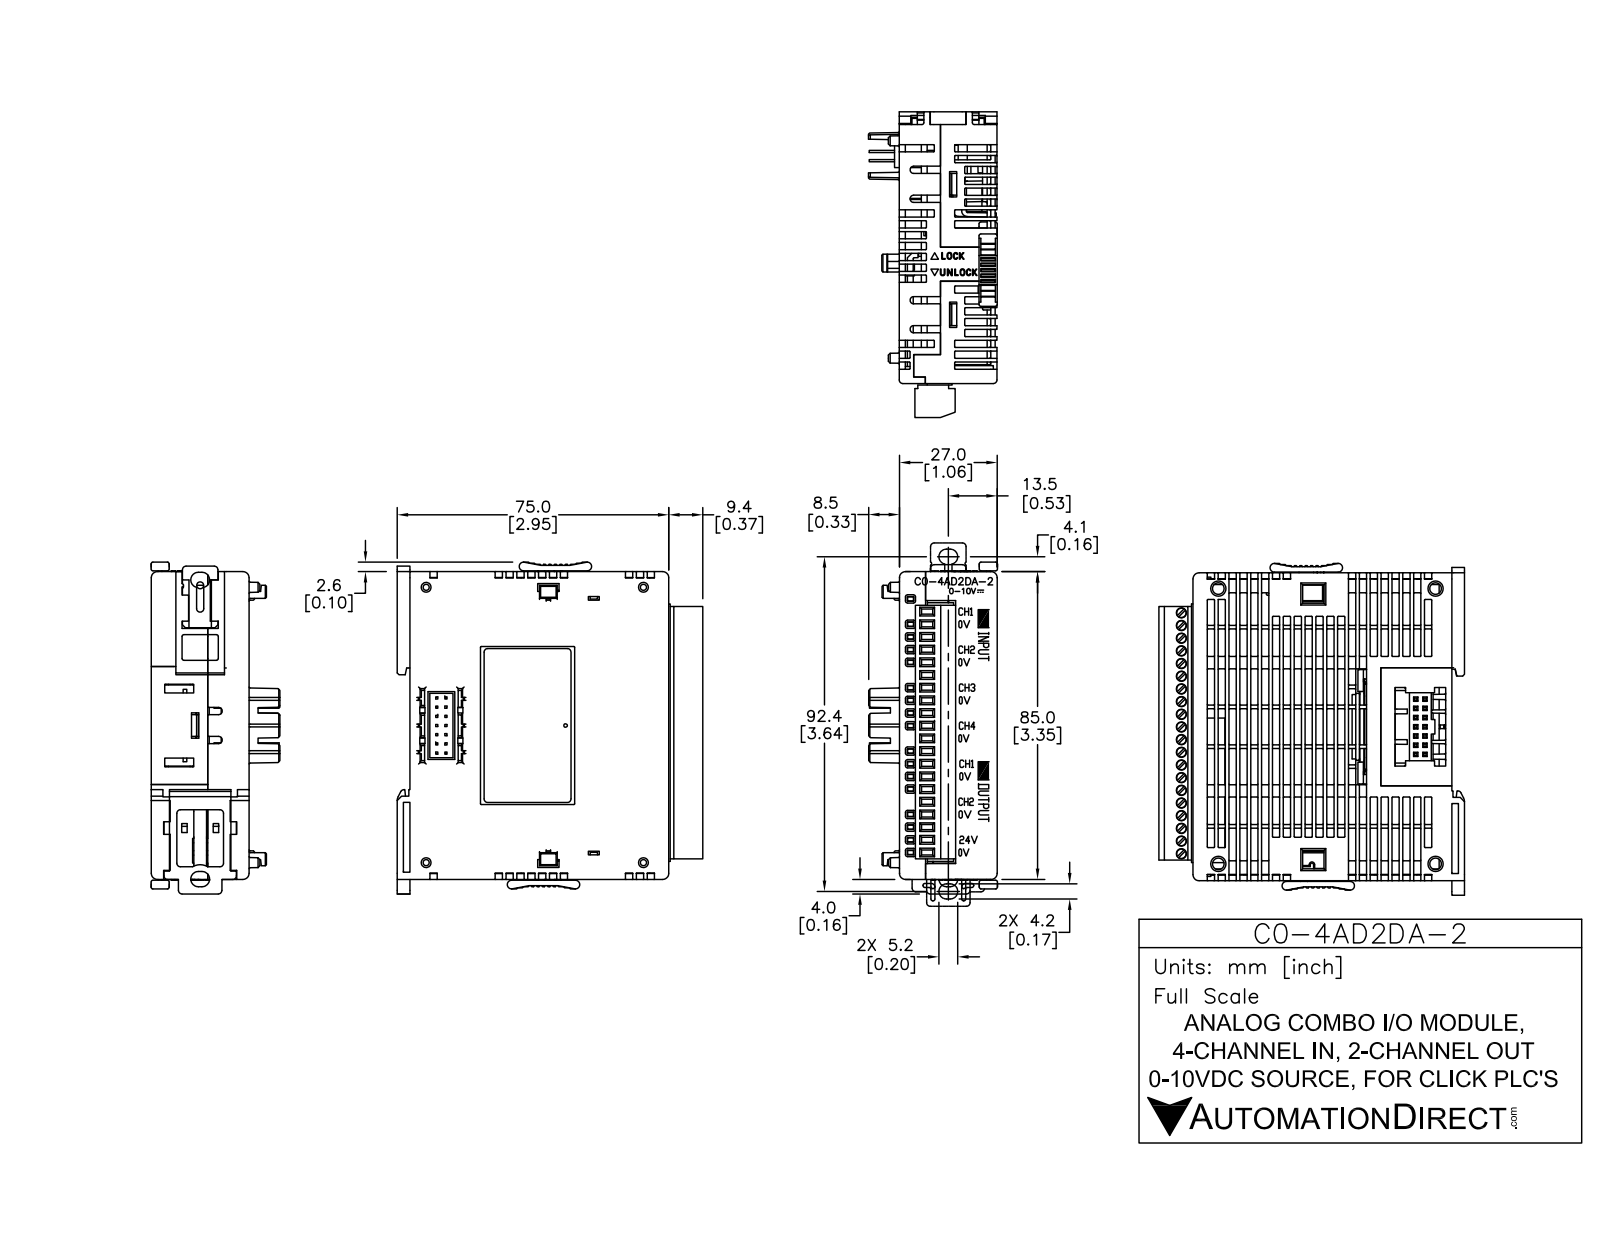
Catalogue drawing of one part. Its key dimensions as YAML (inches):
part_name: "C0-4AD2DA-2"
step_written_by: "SolidWorks 2013 (AUTOMOTIVE_DESIGN)"
units: inches
bodies: {solids: 1, faces: 4130, planar: 2924, cylindrical: 1037, other: 169}
overall_size: [3.606, 3.323, 1.4]
volume: 10.07
surface_area: 52.14
round_holes:
  - {diameter: 0.039, count: 20}
  - {diameter: 0.11, count: 20}
  - {diameter: 0.126, count: 4}
  - {diameter: 0.079, count: 2}
round_bosses_or_shafts:
  - {diameter: 0.102, count: 20}
  - {diameter: 0.075, count: 1}
partial_cylinders:
  - {radius: 0.008, count: 570}
  - {radius: 0.02, count: 43}
  - {radius: 0.012, count: 22}
  - {radius: 0.11, count: 20}
  - {radius: 0.039, count: 18}
  - {radius: 0.047, count: 12}
  - {radius: 0.067, count: 6}
  - {radius: 0.083, count: 4}
face_to_face_distances: [0.02, 1.063, 0.02, 1.043, 2.815, 3.346, 0.067, 1.035, 1.056, 0.138]
hole_center_spacings: [0.138, 0.276, 0.413, 0.551, 0.689, 0.827, 0.965, 1.102]
